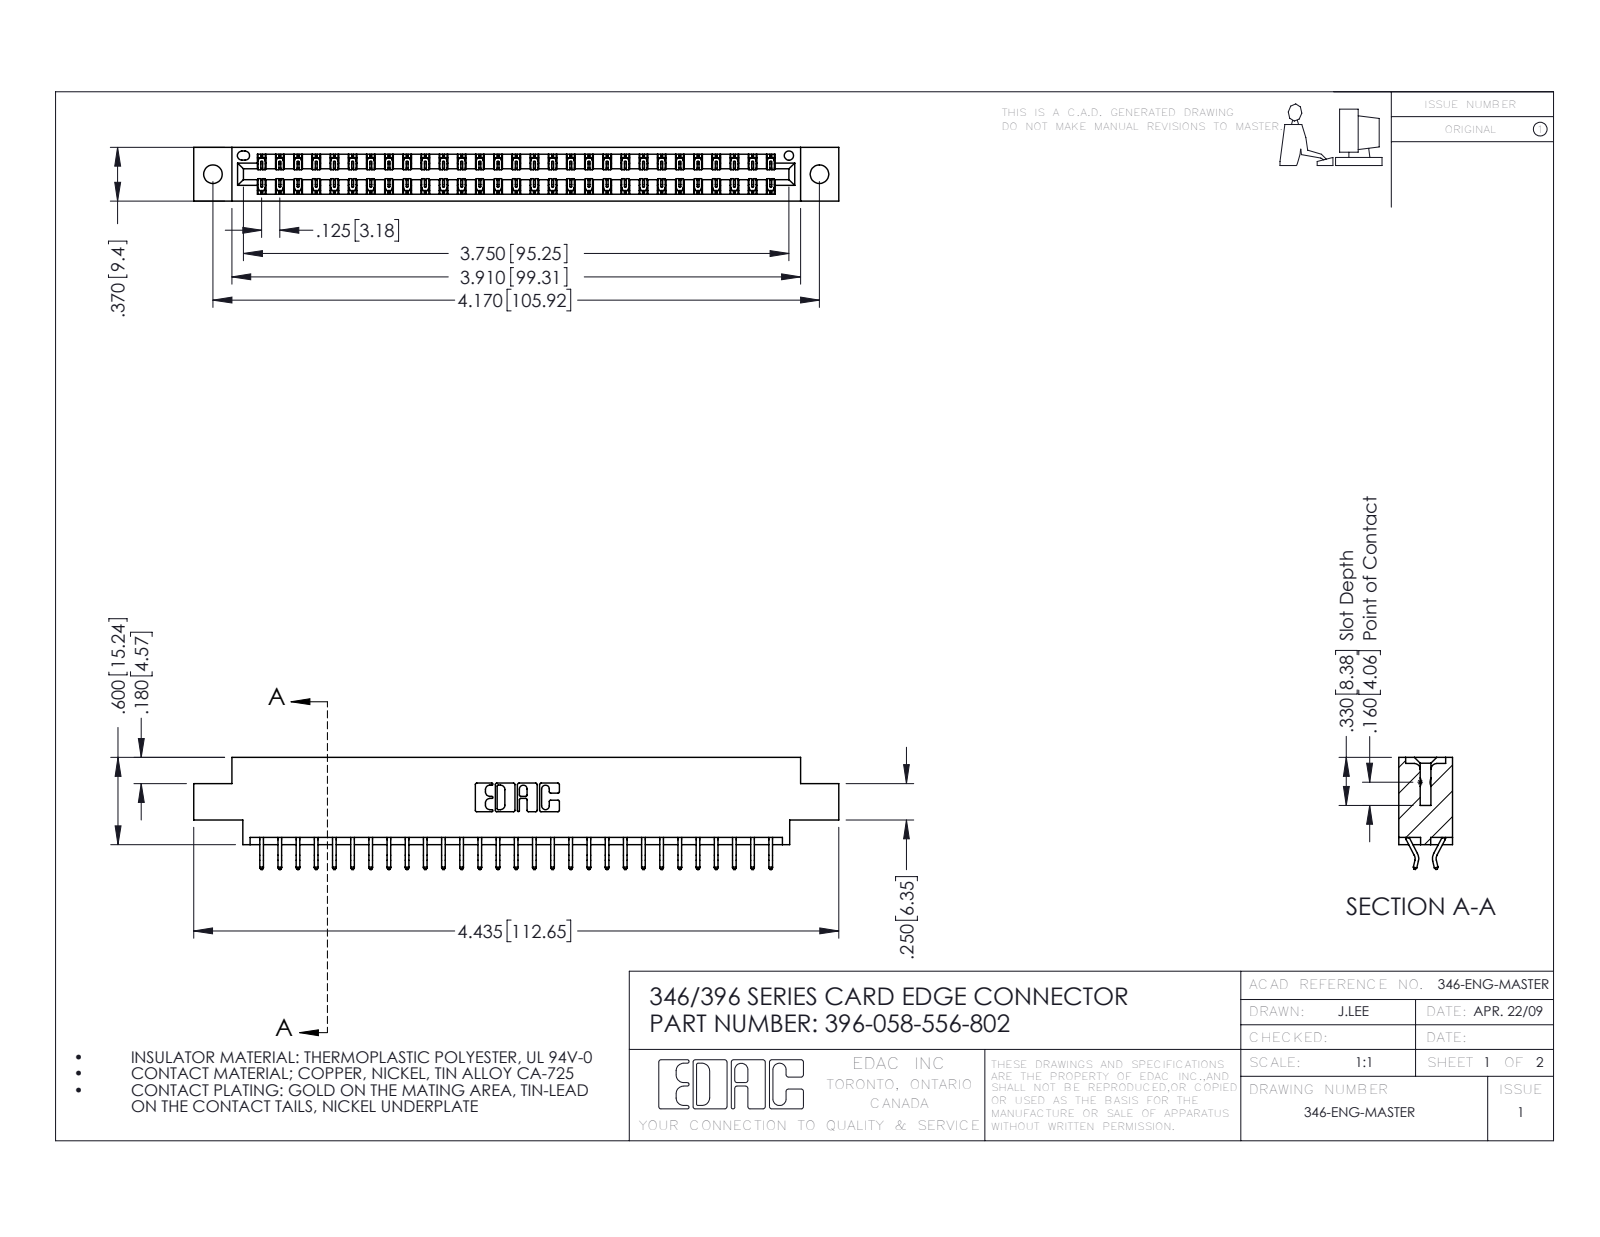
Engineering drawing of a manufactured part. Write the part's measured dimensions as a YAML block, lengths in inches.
part_name: "396-058-556-802; 346 Part_0.170 Offset - 0.128 Dia; 345-292-001_556 Tail"
step_written_by: "SolidWorks 2016 (CONFIG_CONTROL_DESIGN)"
units: inches
bodies: {solids: 59, faces: 3490, planar: 2342, cylindrical: 1148, other: 0}
overall_size: [4.435, 0.77, 0.37]
volume: 0.652
surface_area: 22.24
round_holes:
  - {diameter: 0.128, count: 2}
  - {diameter: 0.064, count: 1}
partial_cylinders:
  - {radius: 0.006, count: 87}
  - {radius: 0.01, count: 22}
  - {radius: 0.007, count: 6}
  - {radius: 0.031, count: 6}
  - {radius: 0.026, count: 3}
  - {radius: 0.01, count: 2}
  - {radius: 0.014, count: 2}
  - {radius: 0.022, count: 2}
face_to_face_distances: [0.048, 0.322, 0.37, 0.25, 0.025, 0.072, 0.298, 0.275, 0.148, 0.222]
hole_center_spacings: [0.246, 3.962, 4.17]
